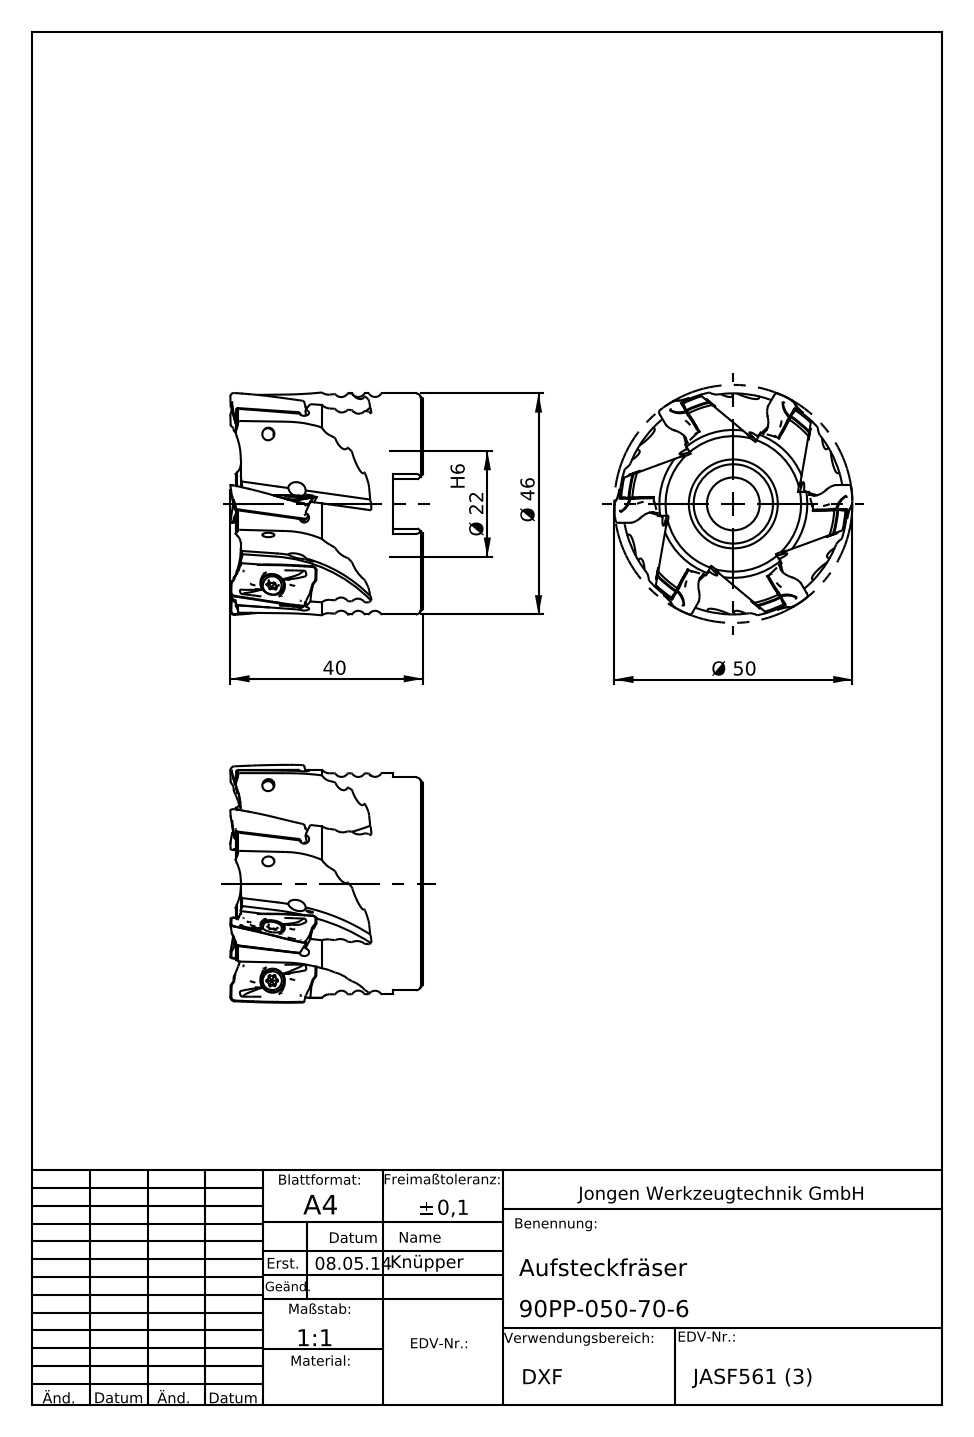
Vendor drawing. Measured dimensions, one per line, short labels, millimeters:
name: 90PP-050-70-6
written by: SolidWorks 2018 (AUTOMOTIVE_DESIGN)
unit: mm
bodies: 1 solid, 439 faces (65 planar, 68 cylindrical, 306 other)
size: 49.99 × 49.99 × 40.05
volume: 51 374 mm³; area: 13 217 mm²
holes: 6× ⌀3, 1× ⌀11, 1× ⌀16.5, 1× ⌀22, 1× ⌀22.15, 1× ⌀22.3
bosses: 1× ⌀46
rounds: 6× R1, 6× R3.54, 6× R5, 1× R23.71
face distances: 37.6, 6.3, 31.3, 23, 16.7, 14.6, 27, 20.7, 4, 10.6
